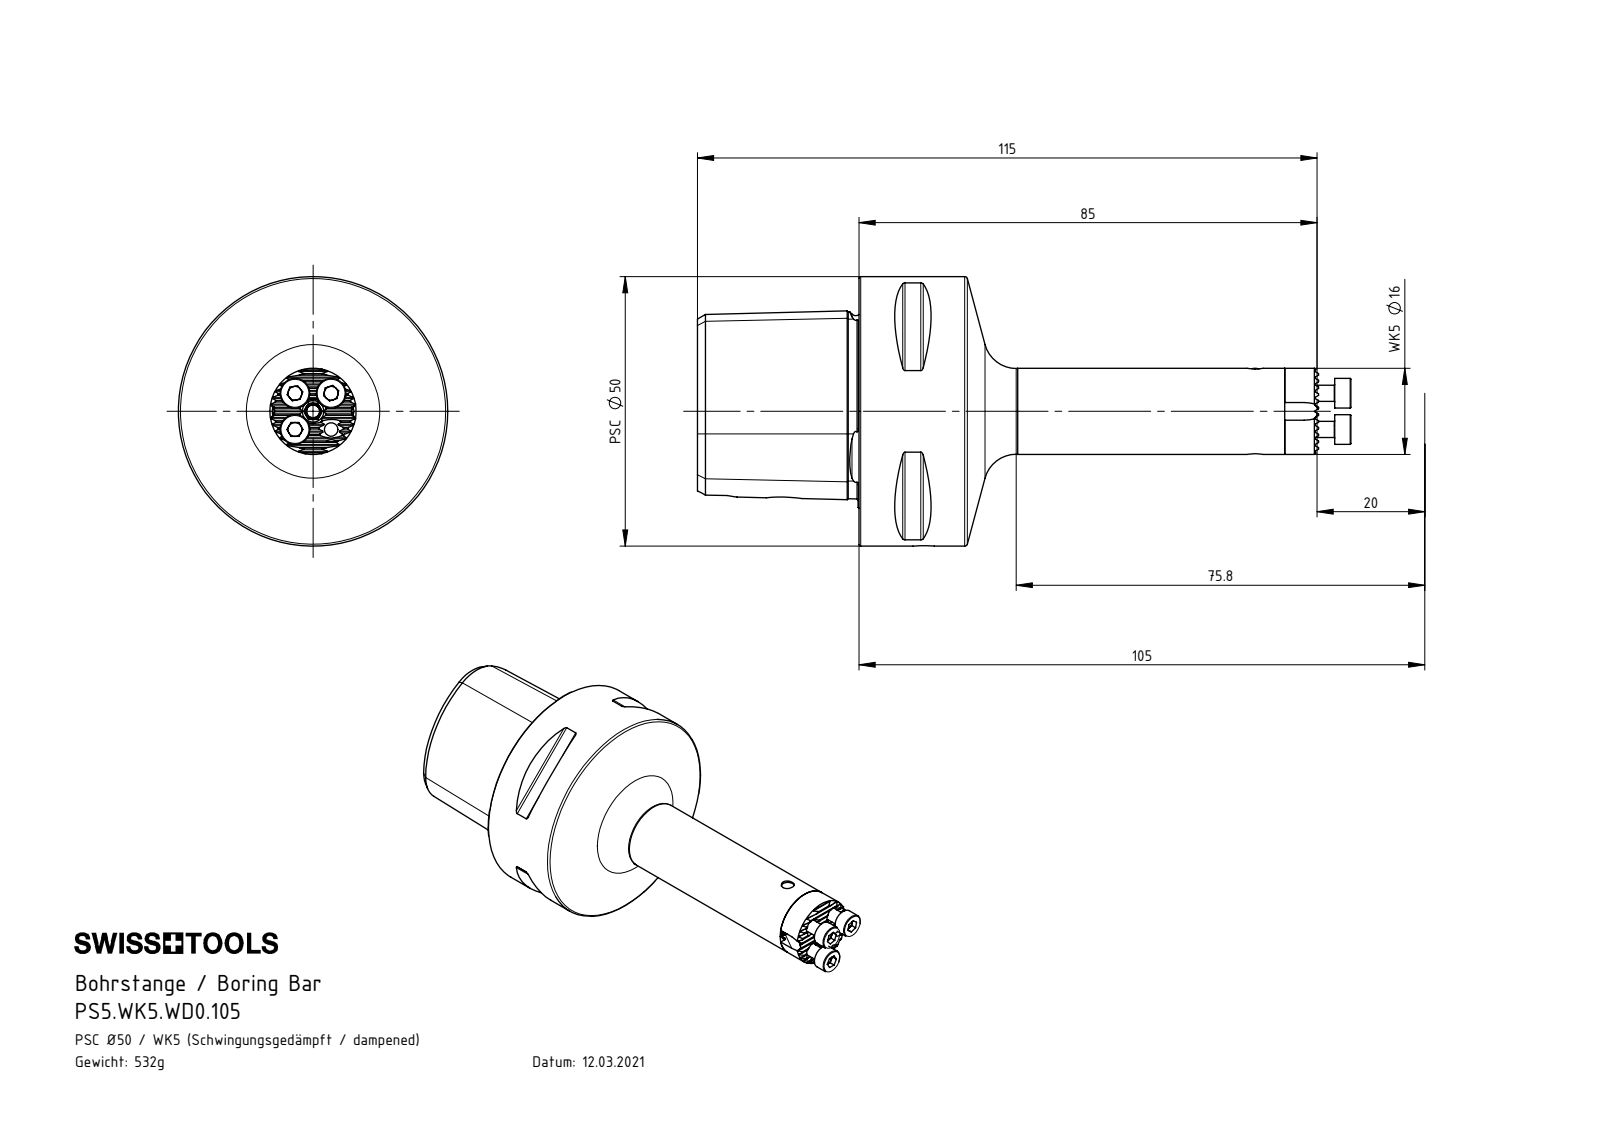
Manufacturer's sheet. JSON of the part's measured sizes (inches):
{"part_name": "WD0-ER1.005.022_A; DIN 3771 - 4x1; WD0-ER1.013.014_A; WD0-ER1.012.030_A (+8 more)", "step_written_by": "SolidWorks 2017 (AUTOMOTIVE_DESIGN)", "units": "inches", "bodies": {"solids": 18, "faces": 479, "planar": 216, "cylindrical": 106, "other": 157}, "overall_size": [4.776, 1.969, 1.969], "volume_in3": 4.167, "surface_area_in2": 38.65, "round_holes": [[0.098, 7], [0.079, 3], [0.118, 2], [0.157, 2], [0.13, 1], [0.177, 1], [0.213, 1], [0.236, 1], [0.24, 1], [0.394, 1], [0.52, 1], [0.571, 1]], "round_bosses_or_shafts": [[0.118, 5], [0.217, 3], [1.969, 1], [0.63, 1], [0.512, 1], [0.496, 1], [0.472, 1], [0.425, 1]], "partial_cylinders_radius": [[0.005, 13], [0.02, 8], [0.065, 4], [0.157, 1]], "face_to_face_distances": [1.181, 0.394, 3.11, 0.755, 0.177, 1.374, 0.118, 1.748, 1.526, 1.496], "hole_center_spacings": [0.187, 0.265, 0.374, 0.295, 0.526, 0.626, 0.921, 0.974]}
